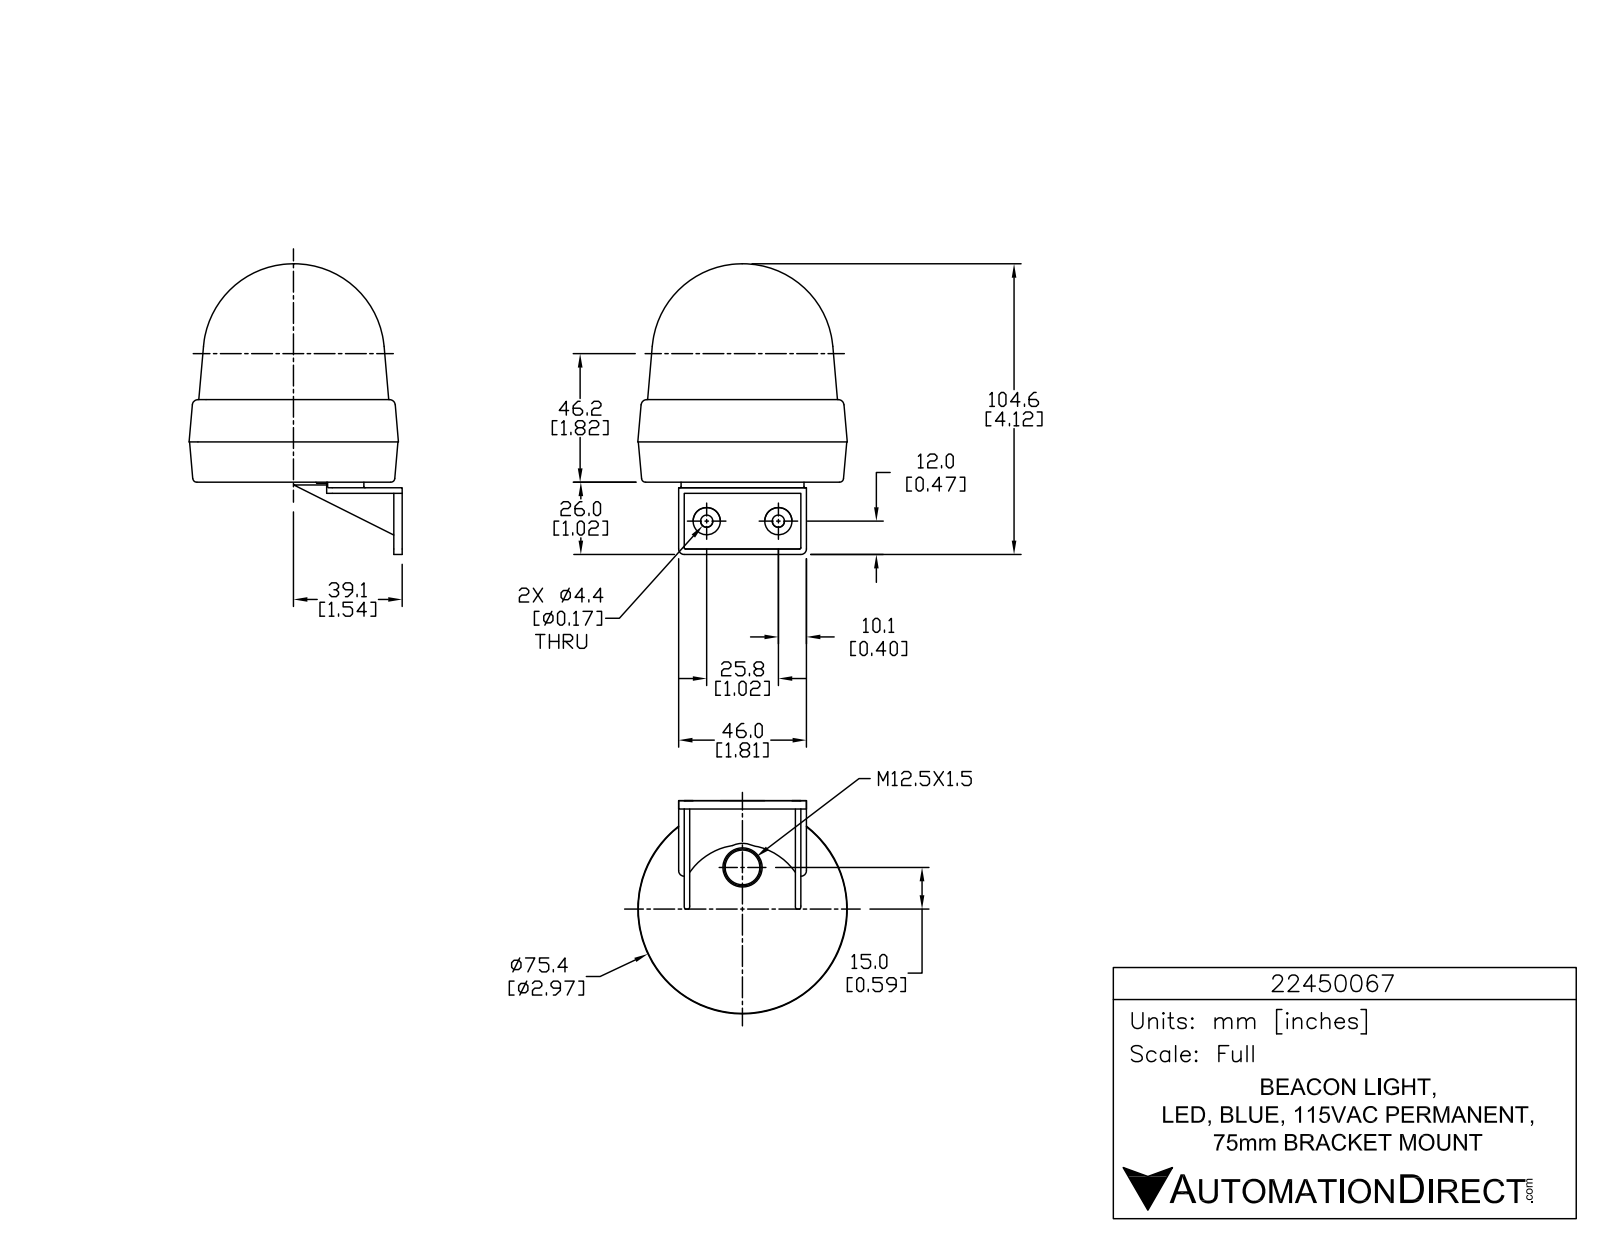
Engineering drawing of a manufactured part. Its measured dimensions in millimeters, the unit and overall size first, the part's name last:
Units: millimetres
Overall size (bounding box): 104.6 × 82.6 × 75.4
Round holes (diameter × count): ⌀1.5 ×3, ⌀4.4 ×2
Round bosses / shafts (diameter × count): ⌀8.6 ×3, ⌀2.1 ×3, ⌀9.8 ×2
Partial cylindrical surfaces — rounded edges, fillets, slot ends (radius × count): R0.1 ×9, R0.1 ×6, R0.3 ×6, R0.3 ×6, R0.3 ×6, R0.5 ×6, R5 ×6, R2 ×4
Main face-to-face distances: 2, 4, 40, 1, 3, 42, 38, 2, 42, 44
Hole centre spacings: 25.8
Volume: 262 500 mm³ · Surface area: 27 080 mm²
Bodies: 1 solid, 819 faces (549 planar, 180 cylindrical, 90 other)
Part name (STEP PRODUCT): 22450067
STEP written by: SolidWorks 2015 (AUTOMOTIVE_DESIGN)
